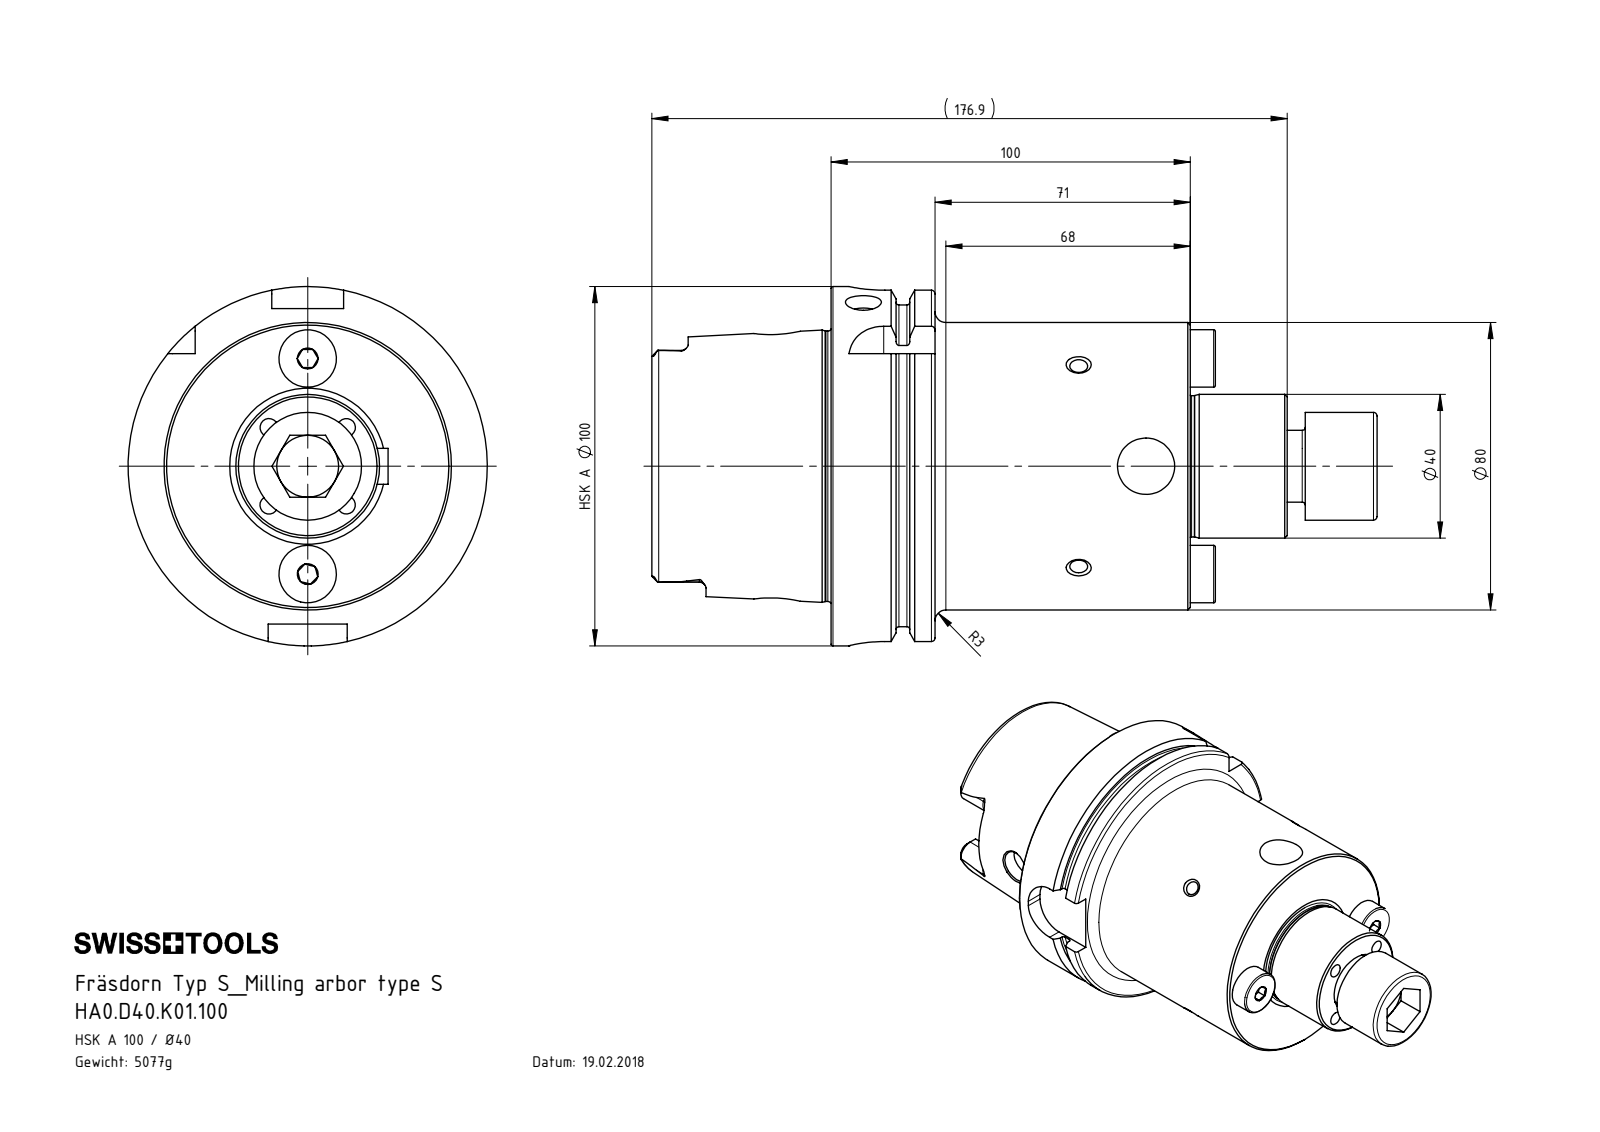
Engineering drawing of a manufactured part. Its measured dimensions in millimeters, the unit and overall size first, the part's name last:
Units: millimetres
Overall size (bounding box): 201.9 × 100 × 100
Round holes (diameter × count): ⌀5 ×12, ⌀10 ×3, ⌀12 ×2, ⌀14 ×2, ⌀17.5 ×1, ⌀21 ×1, ⌀22.5 ×1, ⌀26 ×1, ⌀53 ×1, ⌀63 ×1
Round bosses / shafts (diameter × count): ⌀16 ×2, ⌀6 ×2, ⌀4.6 ×2, ⌀100 ×1, ⌀91.95 ×1, ⌀80 ×1, ⌀75.26 ×1, ⌀40 ×1
Partial cylindrical surfaces — rounded edges, fillets, slot ends (radius × count): R1.9 ×6, R4.88 ×4, R5 ×4, R10 ×4
Main face-to-face distances: 100, 28.95, 71.05, 12.45, 16.5, 87.55, 49.9, 62.35, 78.85, 149.9
Hole centre spacings: 15.25, 20.05, 21.56, 22.04, 42.18, 30, 30.49, 60
Volume: 646 752 mm³ · Surface area: 90 083 mm²
Bodies: 5 solids, 369 faces (89 planar, 119 cylindrical, 161 other)
Part name (STEP PRODUCT): D40-ER1.002.040_A; D40-ER2.001.023_B; DIN 6885 - 10x8x20; HA0-D40.K01.100_D_Fertigbearbeitung (+1 more)
STEP written by: SolidWorks 2017 (AUTOMOTIVE_DESIGN)
